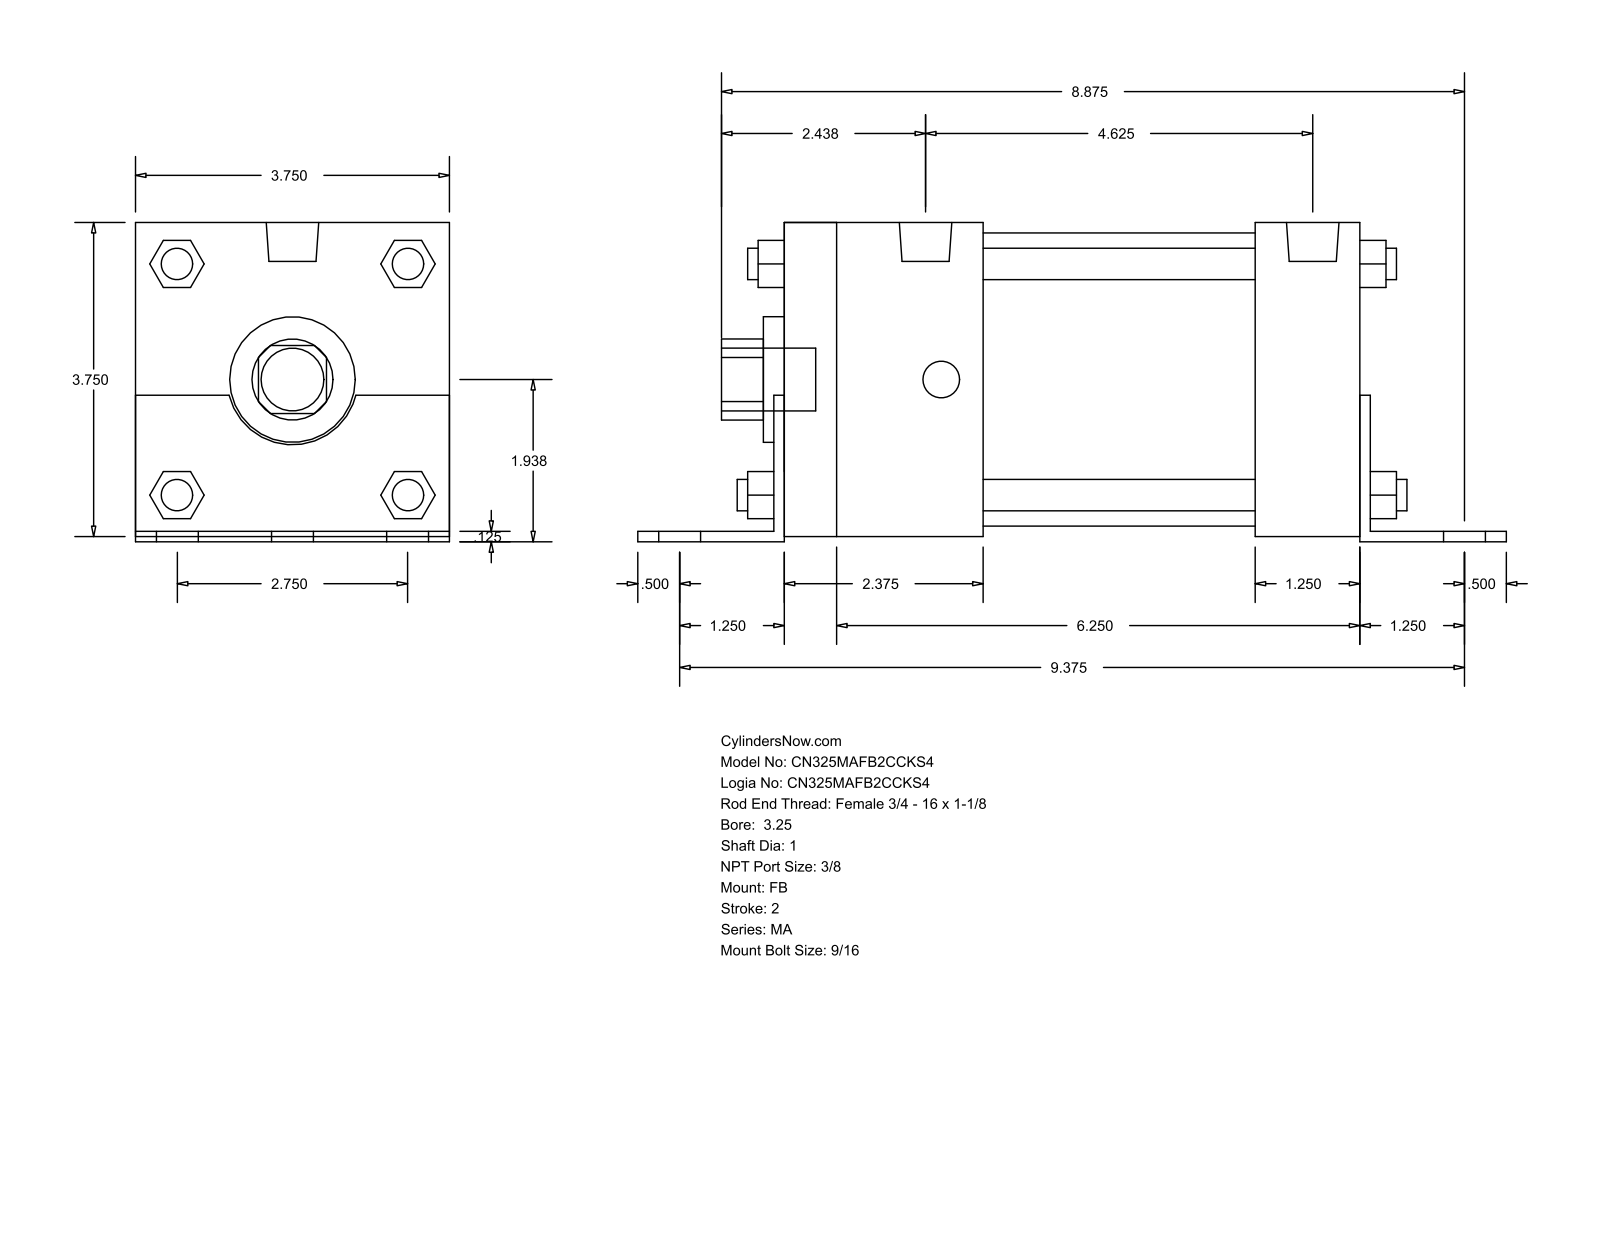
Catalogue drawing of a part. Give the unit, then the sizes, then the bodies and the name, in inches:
Units: inches
Overall size (bounding box): 10.375 × 3.813 × 3.75
Round holes (diameter × count): ⌀1 ×1, ⌀1.5 ×1, ⌀3.5 ×1
Round bosses / shafts (diameter × count): ⌀0.563 ×6, ⌀0.437 ×4, ⌀0.375 ×4, ⌀0.627 ×2, ⌀0.75 ×1
Partial cylindrical surfaces — rounded edges, fillets, slot ends (radius × count): R0.484 ×1, R0.78 ×1
Main face-to-face distances: 3.75, 0.125, 0.063, 3.812, 0.062, 3.687, 7, 6.875, 7.125, 5.75
Bodies: 0 solids, 140 faces (105 planar, 35 cylindrical, 0 other)
Part name (STEP PRODUCT): MA_FB__0325_1
STEP written by: GSSL Pune (CONFIG_CONTROL_DESIGN)
